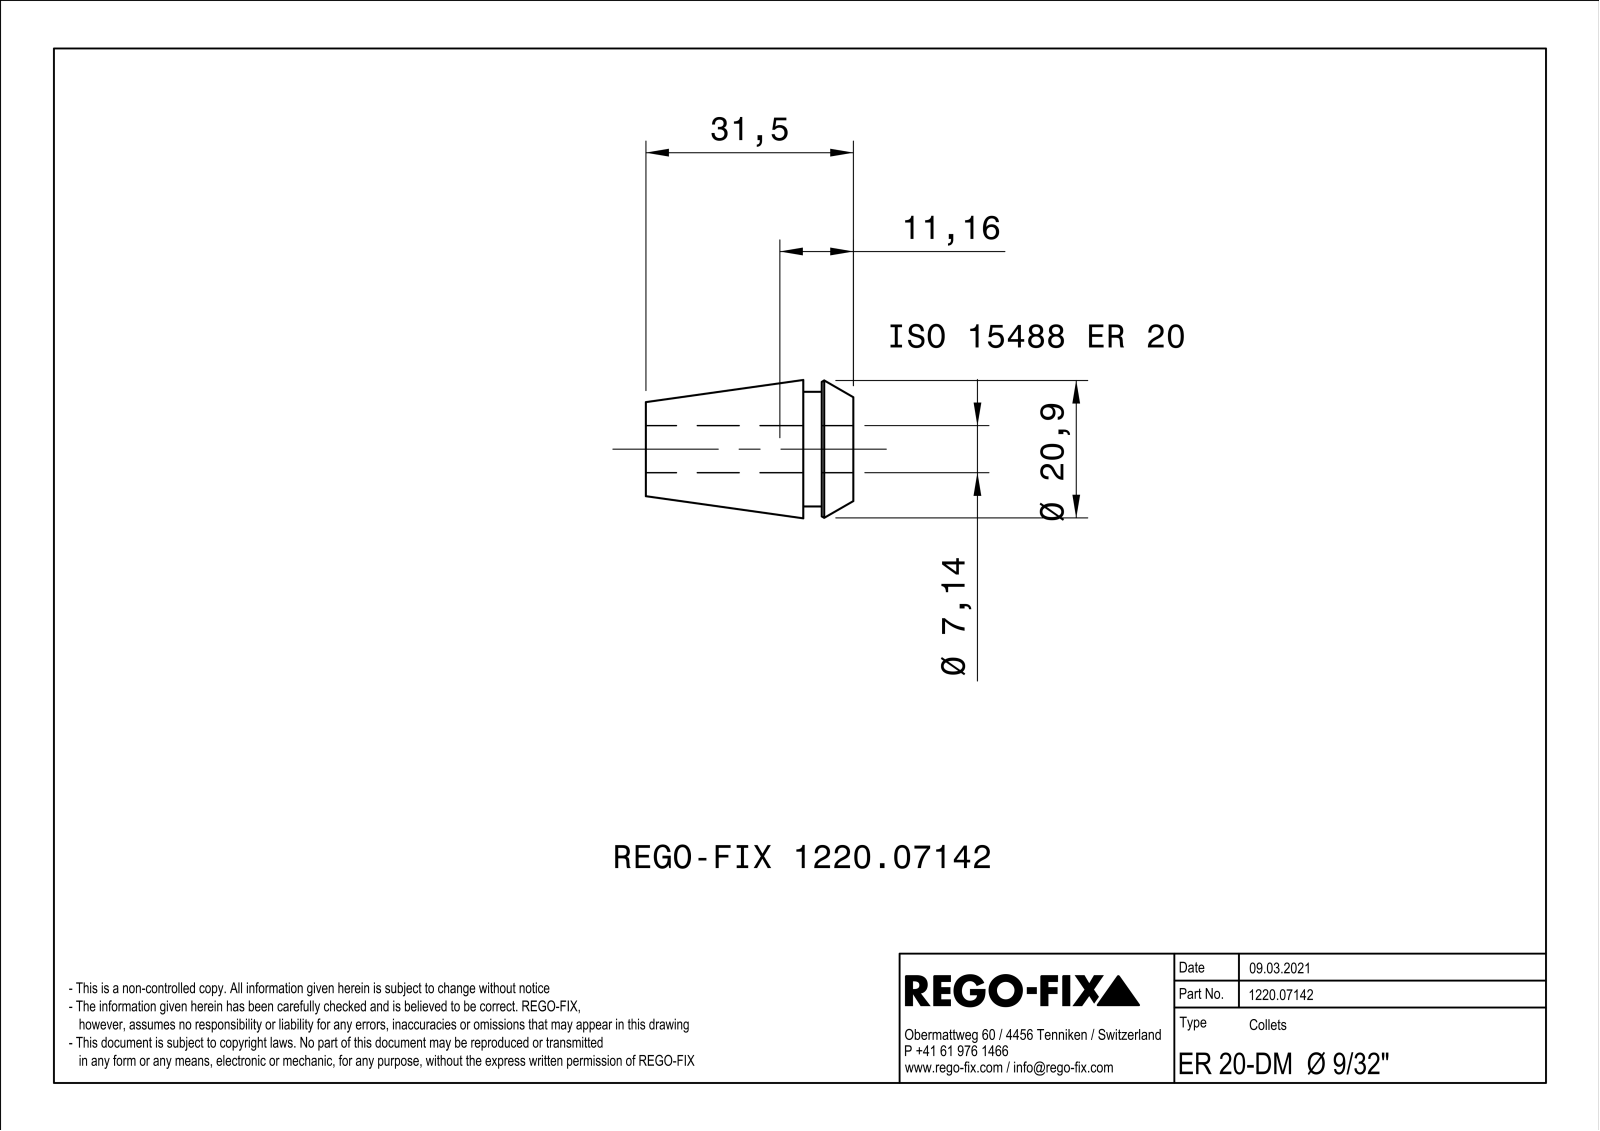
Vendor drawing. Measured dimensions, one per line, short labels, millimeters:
name: NOCUT
written by: SIEMENS PLM Software Solid Edge ST10 (AUTOMOTIVE_DESIGN)
unit: mm
bodies: 1 solid, 154 faces (80 planar, 9 cylindrical, 65 other)
size: 31.5 × 20.99 × 20.99
volume: 5 502 mm³; area: 6 252 mm²
holes: 1× ⌀7.14
bosses: 1× ⌀17.4
face distances: 0.6, 7.6, 31.5, 23.9, 4.8, 2.8, 26.7, 14, 9.2, 6.4
